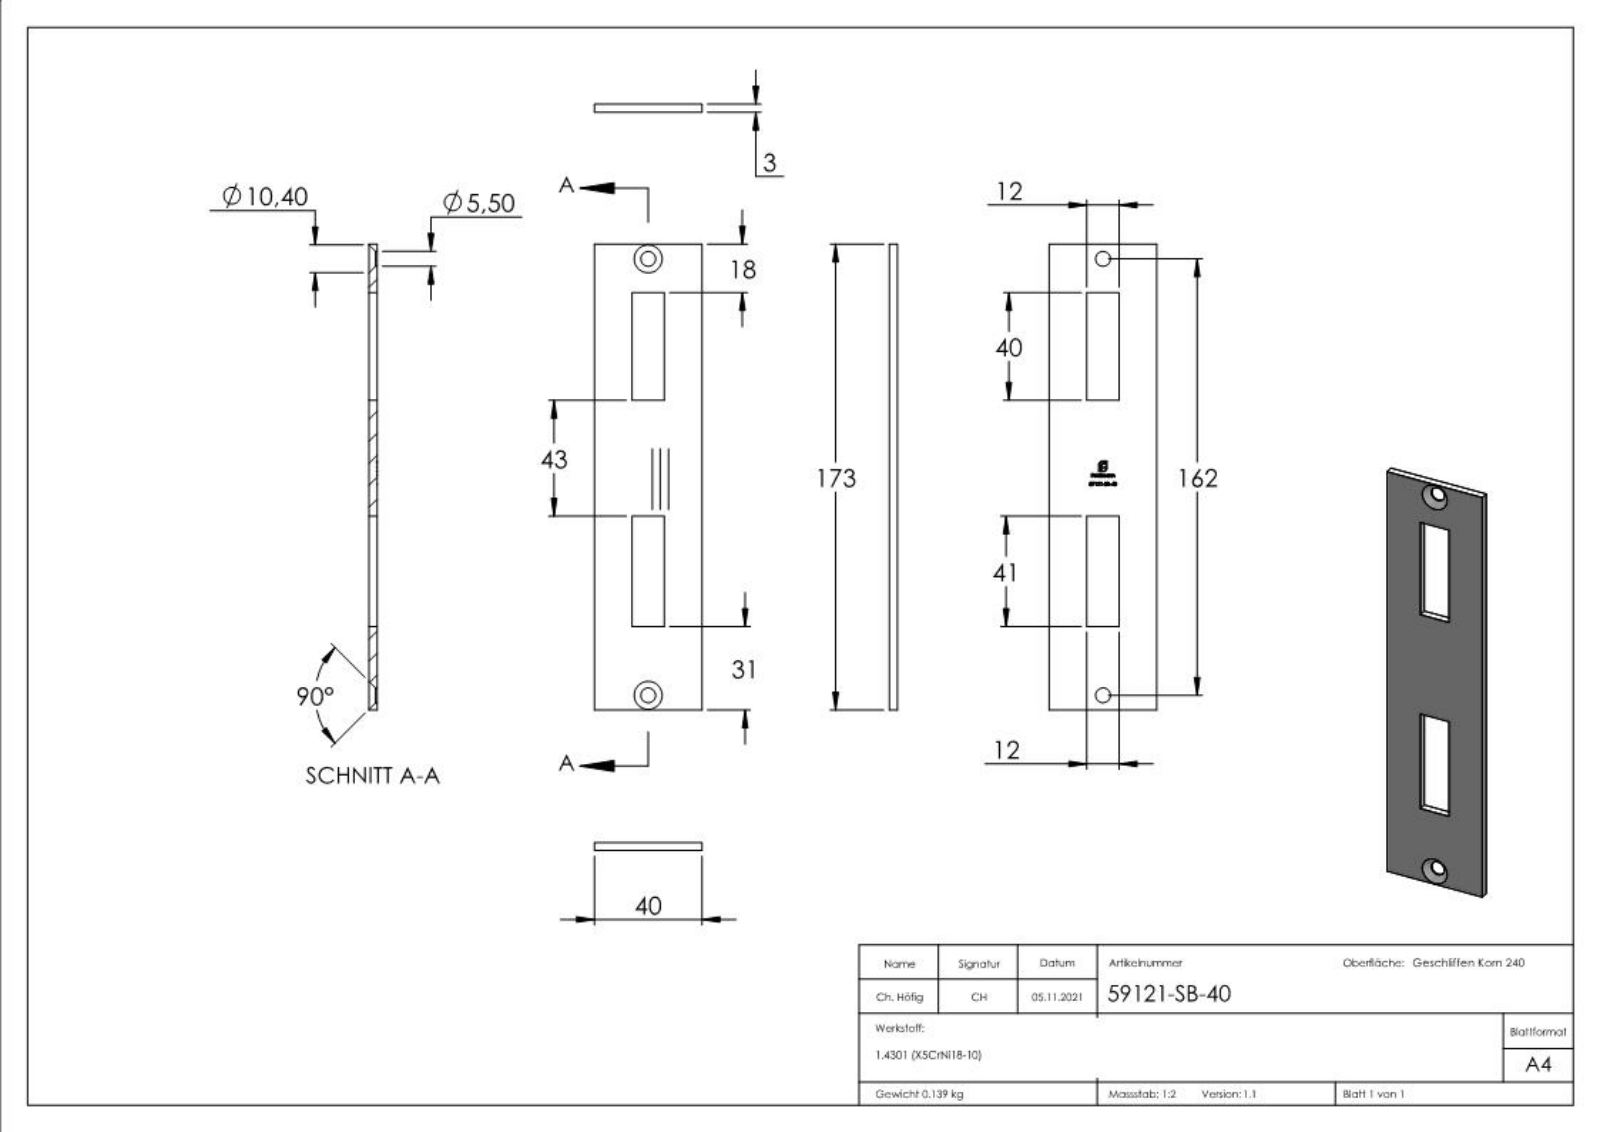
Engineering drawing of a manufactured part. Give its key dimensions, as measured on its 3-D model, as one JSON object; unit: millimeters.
{"part_name": "59121-SB-40", "step_written_by": "SolidWorks 2018 (CONFIG_CONTROL_DESIGN)", "units": "millimeters", "bodies": {"solids": 1, "faces": 305, "planar": 177, "cylindrical": 2, "other": 126}, "overall_size": [173, 40, 3], "volume_mm3": 17566, "surface_area_mm2": 13792, "round_holes": [[5.5, 2]], "face_to_face_distances": [3, 40, 14, 26, 12, 173, 31, 72, 115, 155], "hole_center_spacings": [162]}
